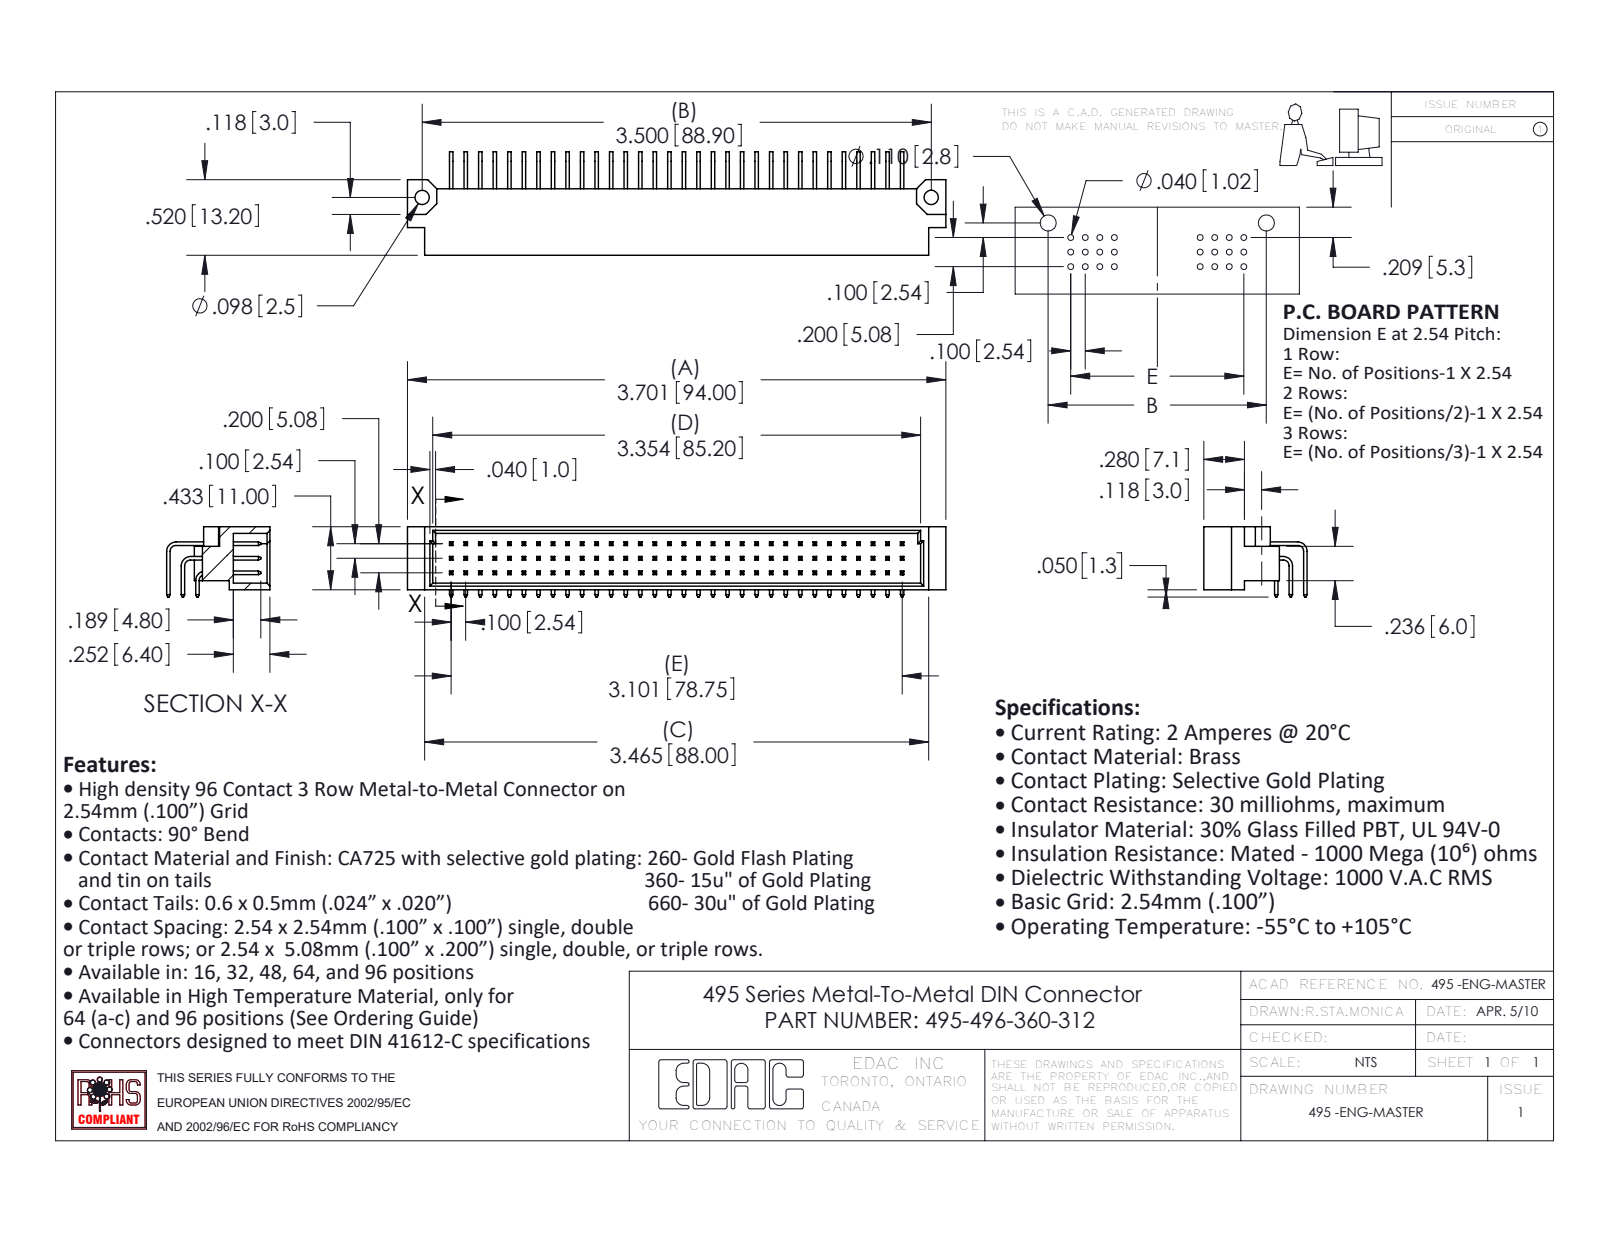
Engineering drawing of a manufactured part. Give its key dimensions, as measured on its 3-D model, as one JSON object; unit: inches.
{"part_name": "495-290-2; 495-290-1; 495-496-360-312; 495-290-3 (+1 more)", "step_written_by": "SolidWorks 2020 (AUTOMOTIVE_DESIGN)", "units": "inches", "bodies": {"solids": 97, "faces": 2161, "planar": 1965, "cylindrical": 196, "other": 0}, "overall_size": [3.701, 0.711, 0.483], "volume_in3": 0.404, "surface_area_in2": 17.74, "round_holes": [[0.098, 2]], "partial_cylinders_radius": [[0.04, 3], [0.065, 3]], "face_to_face_distances": [0.1, 0.024, 0.2, 0.205, 0.045, 0.388, 0.124, 0.076, 0.433, 0.343], "hole_center_spacings": [3.5]}
